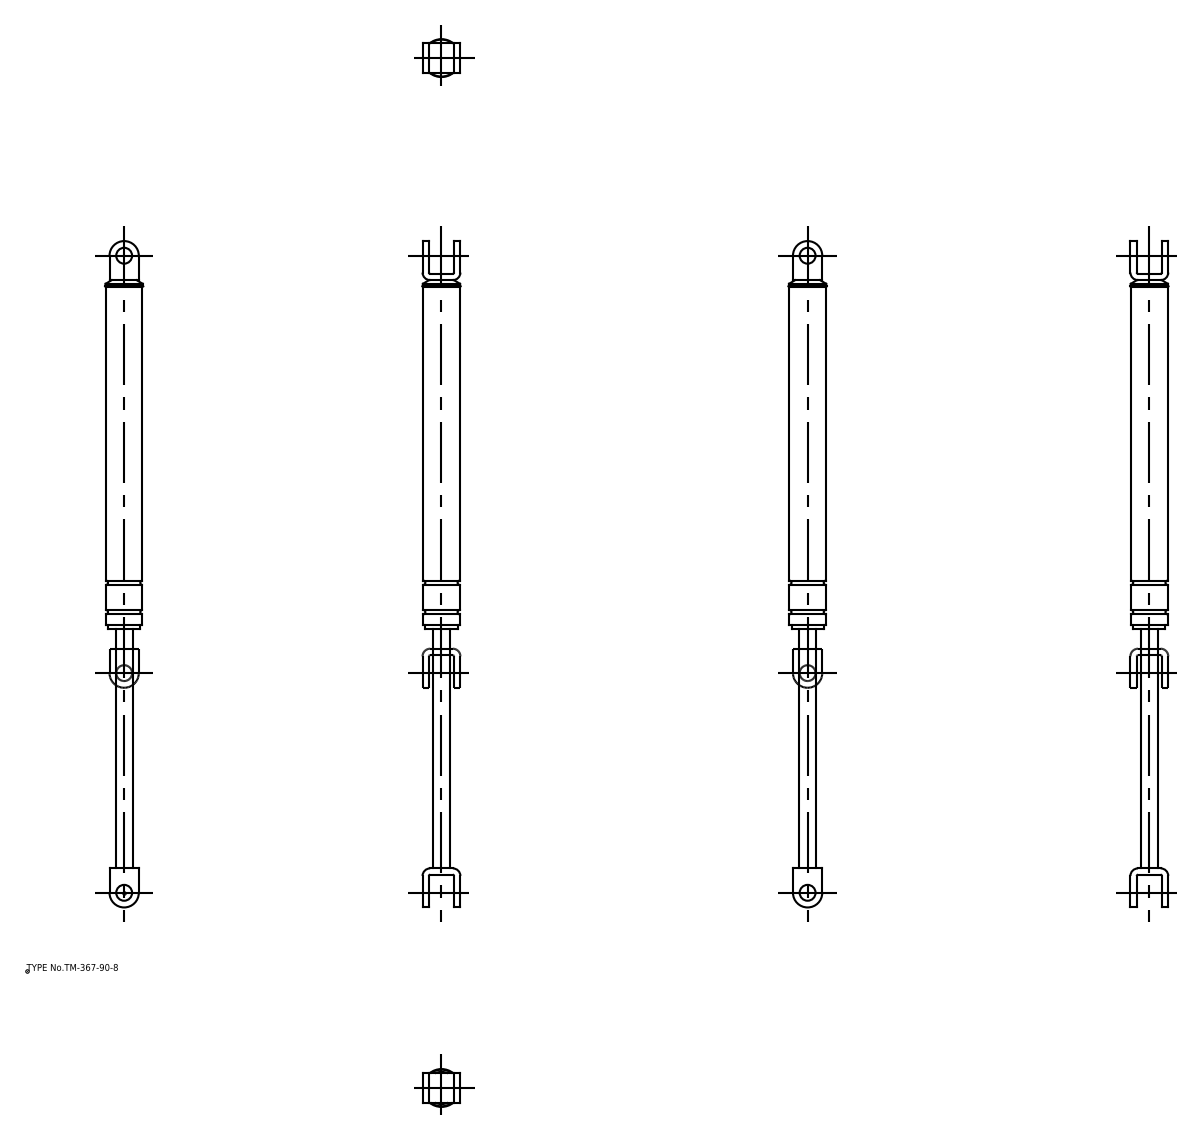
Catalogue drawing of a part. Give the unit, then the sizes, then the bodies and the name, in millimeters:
Units: millimetres
Overall size (bounding box): 273 × 15.5 × 15.5
Round holes (diameter × count): ⌀6.5 ×2
Round bosses / shafts (diameter × count): ⌀15 ×1, ⌀13.2 ×1, ⌀7 ×1
Partial cylindrical surfaces — rounded edges, fillets, slot ends (radius × count): R0.5 ×4, R3.1 ×4, R6 ×2
Main face-to-face distances: 2.6, 12.9, 10.3, 15.5, 12, 100.6, 246.2, 145.6, 243.6, 98
Hole centre spacings: 261
Volume: 30 837 mm³ · Surface area: 11 387 mm²
Bodies: 2 solids, 62 faces (22 planar, 30 cylindrical, 10 other)
Part name (STEP PRODUCT): TM_367_90_8; TM_367_90_8_div
STEP written by: spGate 16.7.1 (AUTOMOTIVE_DESIGN)
